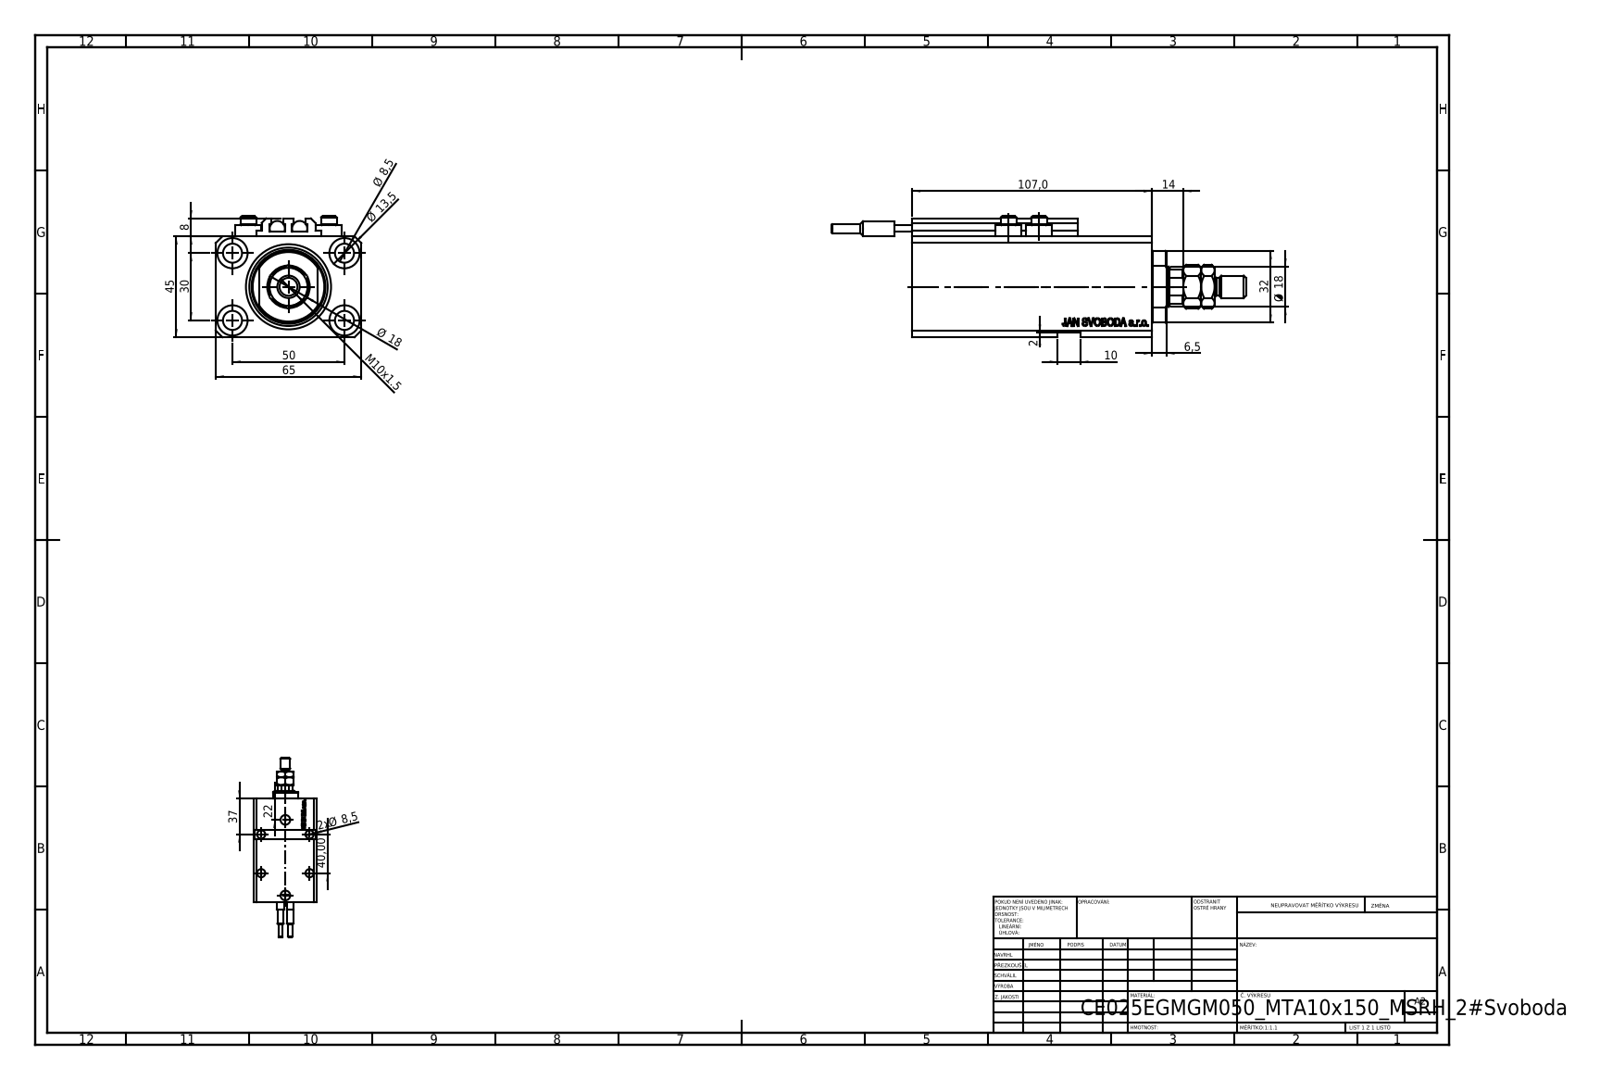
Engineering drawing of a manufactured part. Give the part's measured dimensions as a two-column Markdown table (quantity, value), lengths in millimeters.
| quantity | value |
| --- | --- |
| part name | V250CE_C_VCP; V250CE_VC_E; V250CE_E_Body; SWITCH_V250CE (+2 more) |
| STEP written by | SolidWorks 2019 (CONFIG_CONTROL_DESIGN) |
| units | millimeters |
| bodies | 11 solids, 1188 faces (558 planar, 162 cylindrical, 468 other) |
| overall size | 185 × 65 × 54 |
| volume | 281 459 mm³ |
| surface area | 81 364 mm² |
| round holes (diameter × count) | 8.5 × 9, 1.25 × 4, 4 × 4, 13.5 × 4, 10 × 2, 13.16 × 2, 20 × 2, 18 × 1, 25 × 1, 38 × 1 |
| round bosses / shafts (diameter × count) | 11.6 × 4, 7 × 4, 6.8 × 2, 6.5 × 2, 4 × 2, 10 × 1, 8 × 1 |
| partial cylindrical surfaces (radius × count) | 0.2 × 10, 8.5 × 1, 16 × 1 |
| main face-to-face distances | 45, 65, 14, 2, 47, 93, 3, 107, 6.9, 10 |
| hole center spacings | 29.15, 50, 13.6, 14.76, 15.12, 27.51, 27.89, 30 |
